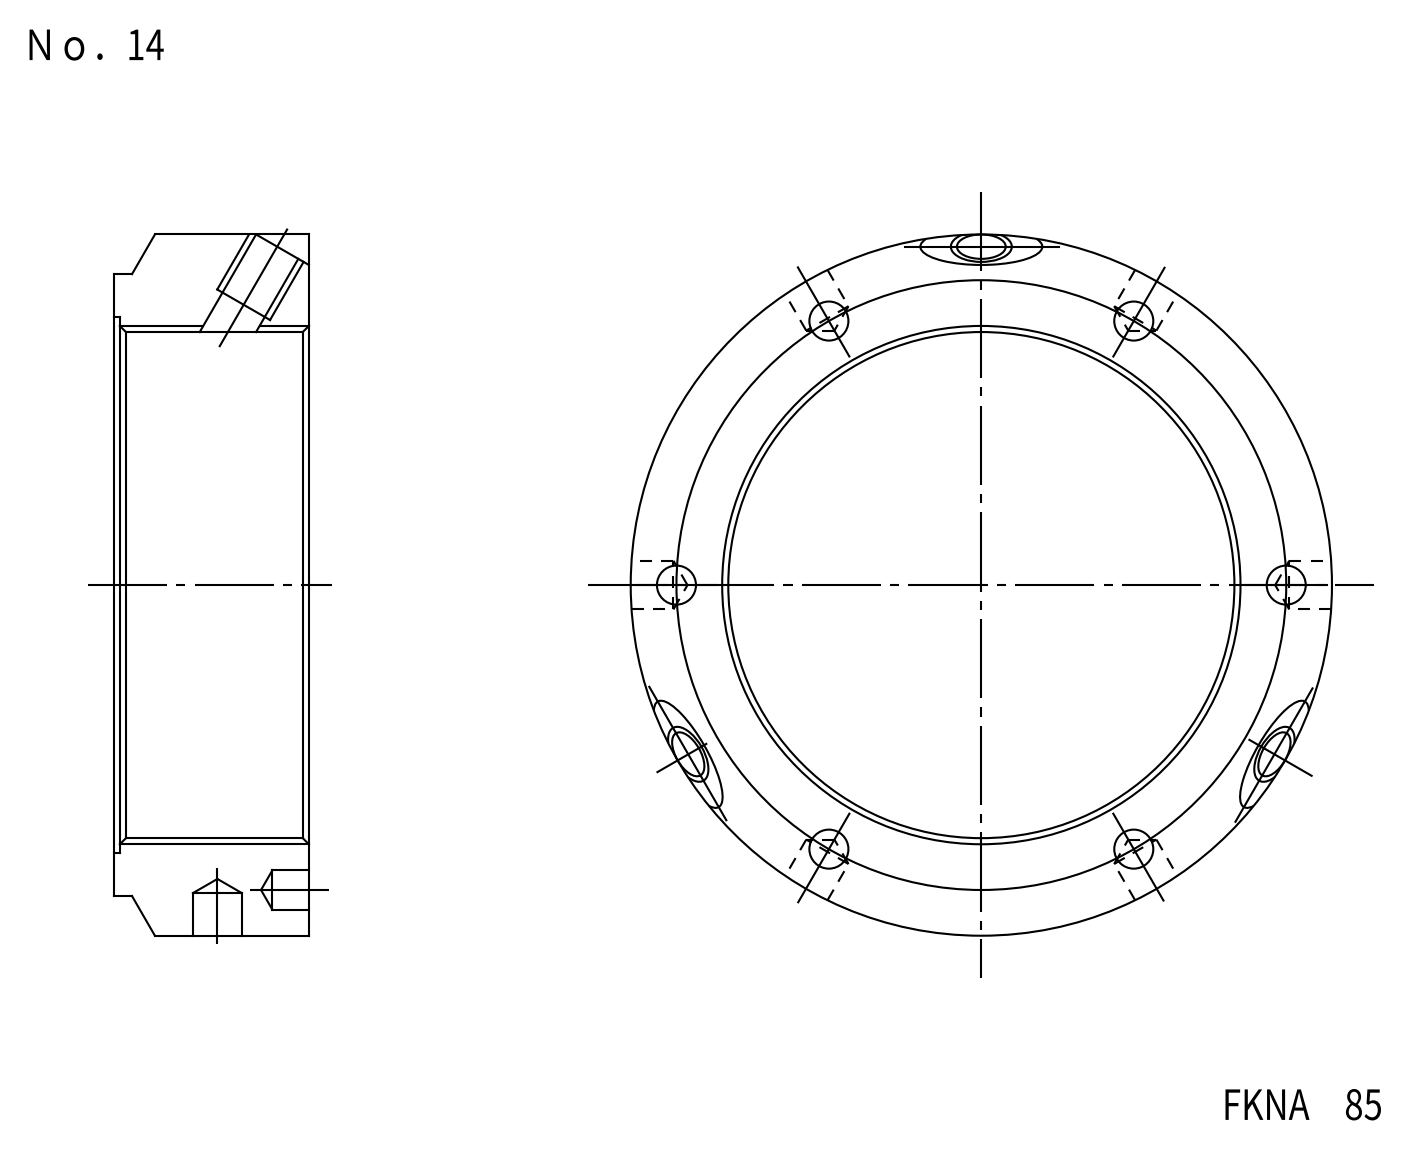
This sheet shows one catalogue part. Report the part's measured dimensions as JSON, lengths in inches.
{"part_name": "FKD FKNA85", "step_written_by": "Autodesk Inventor LT (CONFIG_CONTROL_DESIGN)", "units": "inches", "bodies": {"solids": 1, "faces": 44, "planar": 6, "cylindrical": 25, "other": 13}, "overall_size": [4.528, 4.528, 1.26], "volume_in3": 8.353, "surface_area_in2": 47.66, "round_holes": [[0.252, 6], [0.315, 3], [0.33, 3], [0.402, 3], [3.346, 1], [3.465, 1]], "round_bosses_or_shafts": [[4.528, 1], [4.016, 1]], "partial_cylinders_radius": [[0.787, 3]], "face_to_face_distances": [1.26, 0.059, 1.201], "hole_center_spacings": [1.969, 3.409, 3.937]}
